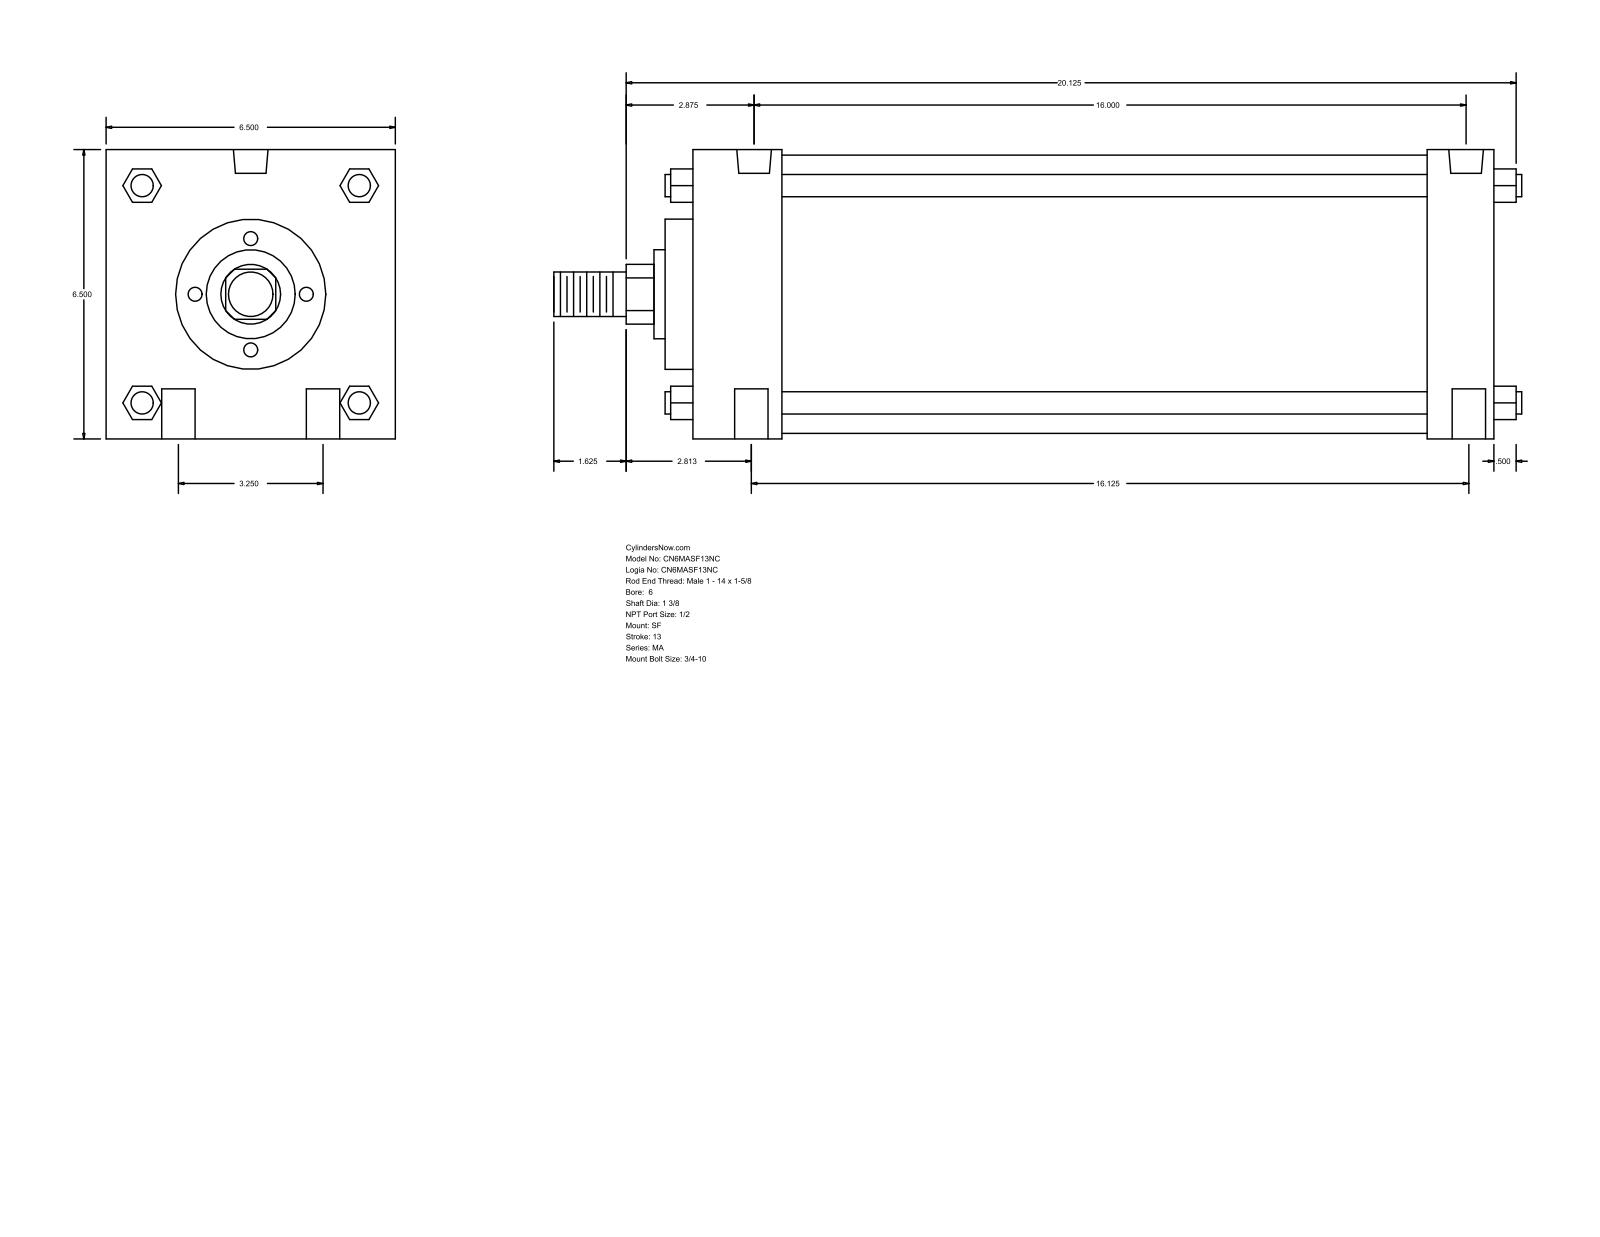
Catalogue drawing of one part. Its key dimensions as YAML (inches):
part_name: "MA_SF__0600_1.375"
step_written_by: "GSSL Pune (CONFIG_CONTROL_DESIGN)"
units: inches
bodies: {solids: 0, faces: 126, planar: 95, cylindrical: 31, other: 0}
overall_size: [21.75, 6.5, 6.5]
round_holes:
  - {diameter: 0.75, count: 4}
  - {diameter: 0.687, count: 2}
  - {diameter: 0.778, count: 2}
round_bosses_or_shafts:
  - {diameter: 0.5, count: 4}
  - {diameter: 6.25, count: 1}
  - {diameter: 3.375, count: 1}
  - {diameter: 2, count: 1}
  - {diameter: 1.375, count: 1}
  - {diameter: 1, count: 1}
partial_cylinders:
  - {radius: 0.672, count: 1}
face_to_face_distances: [6.5, 18, 16.5, 2, 1.5, 14.5, 16, 2.625, 0.625, 17.125]
hole_center_spacings: [1.626, 3.25, 16, 16.125, 16.144, 16.144, 16.449]
